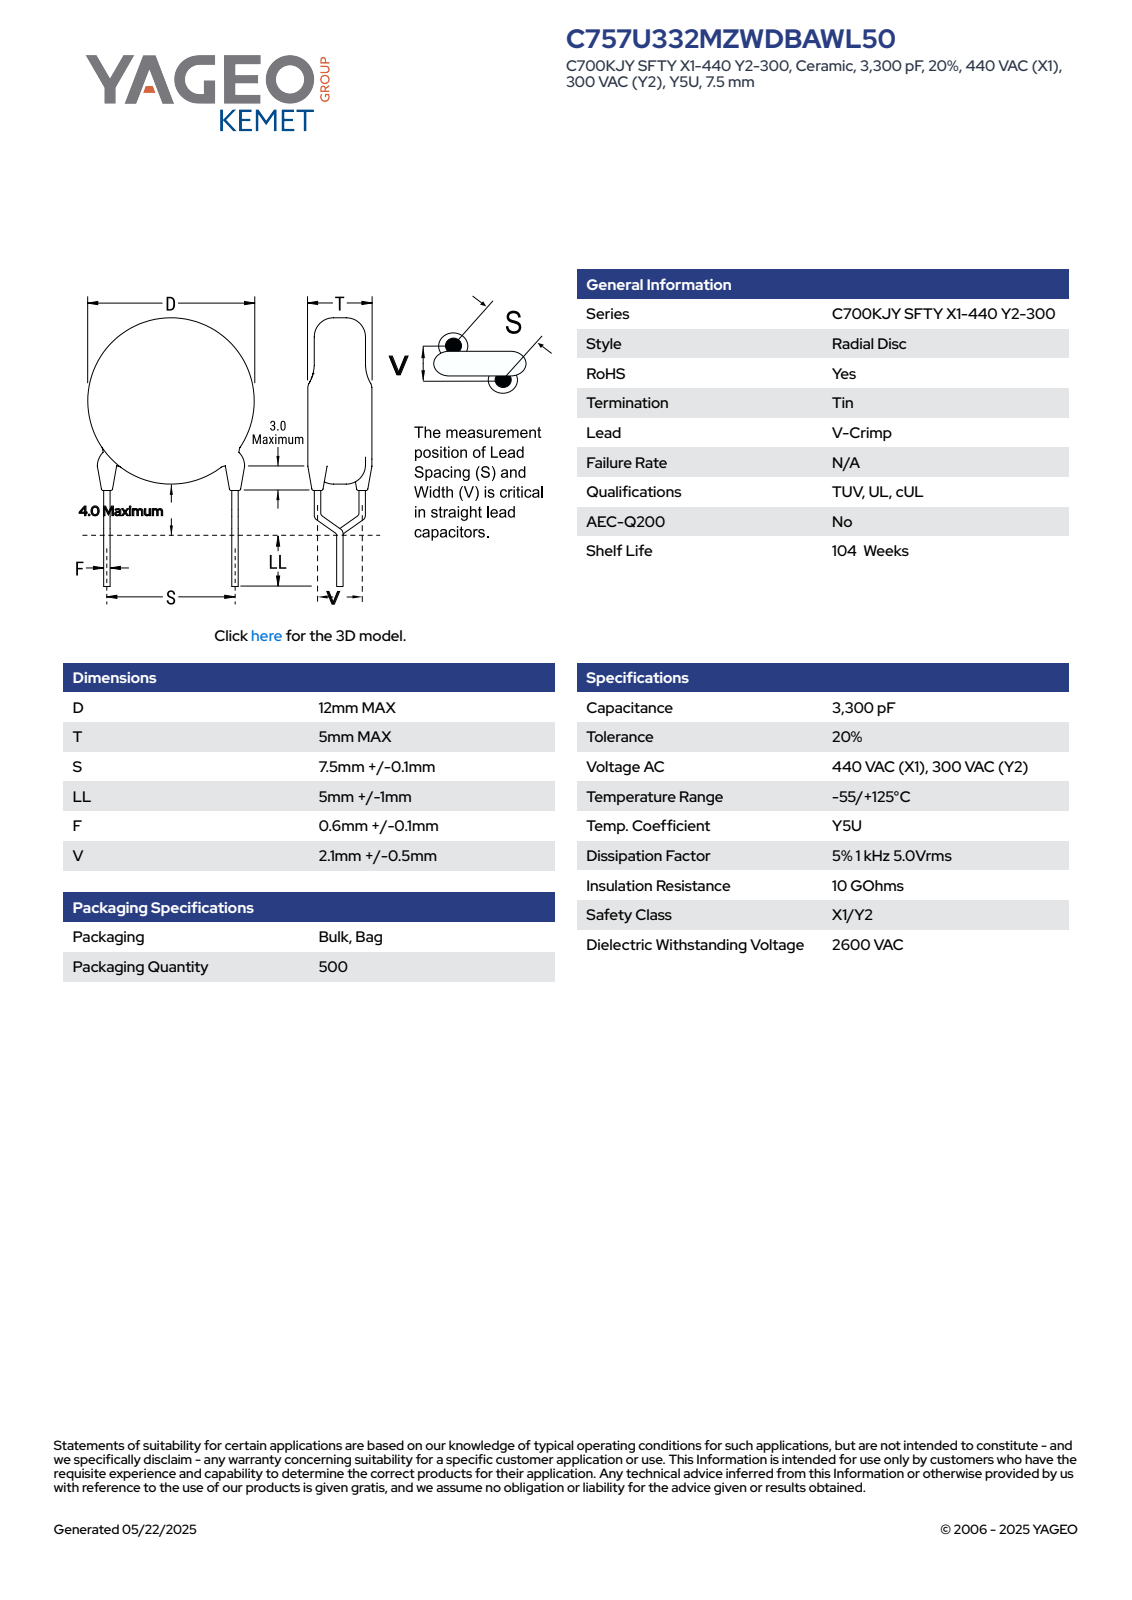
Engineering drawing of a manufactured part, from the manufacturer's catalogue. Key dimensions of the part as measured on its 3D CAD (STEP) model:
Part name (STEP PRODUCT): CCD_VC12X5_D12T5S7.5LL6F0.7V2.1
STEP written by: SolidWorks 2021 (AUTOMOTIVE_DESIGN)
Units: millimetres
Bodies: 4 solids, 85 faces (63 planar, 18 cylindrical, 4 other)
Overall size (bounding box): 18 × 12.16 × 5
Volume: 558 mm³ · Surface area: 442 mm²
Round bosses / shafts (diameter × count): ⌀0.7 ×6, ⌀1.2 ×2, ⌀12 ×1
Main face-to-face distances: 5, 6, 13.43, 7.43, 11.5, 5.5, 1.93, 0.53, 0.36, 7.93
